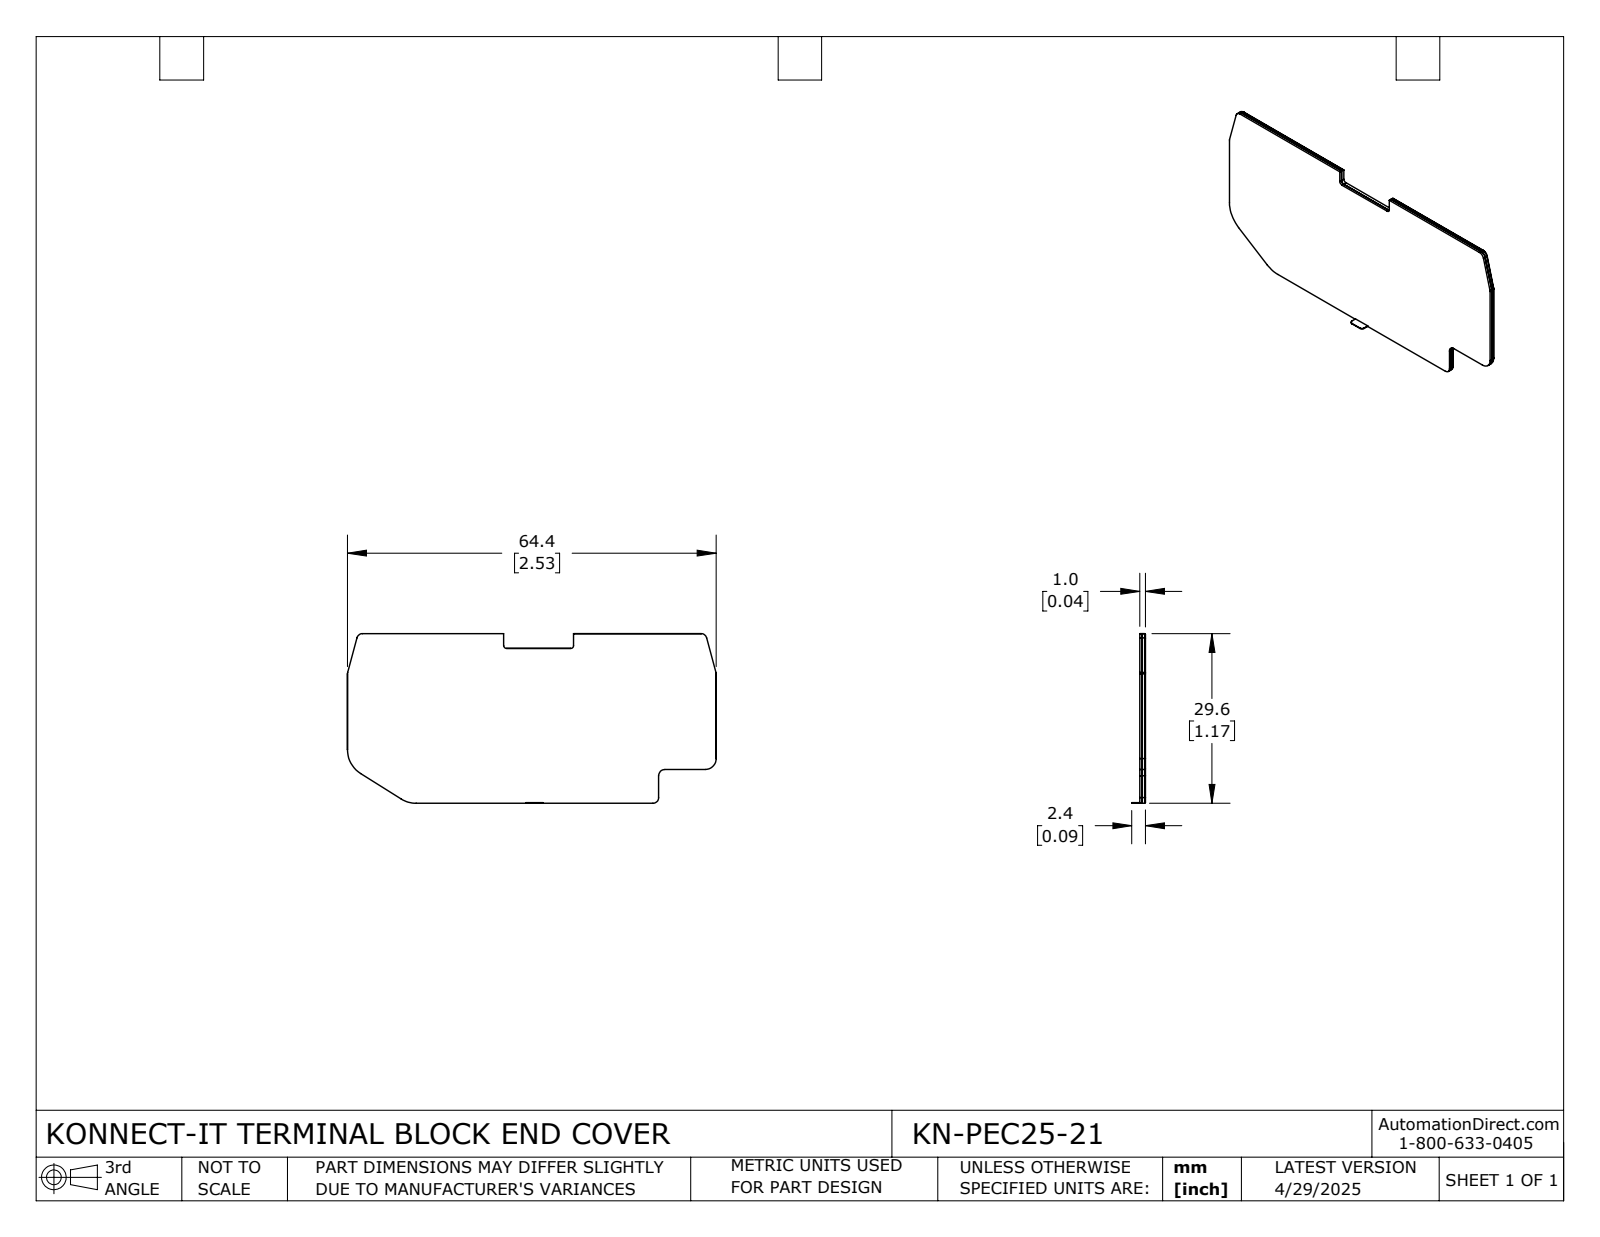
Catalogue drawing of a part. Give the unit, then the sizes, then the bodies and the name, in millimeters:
Units: millimetres
Overall size (bounding box): 64.37 × 29.61 × 2.4
Partial cylindrical surfaces — rounded edges, fillets, slot ends (radius × count): R0.9 ×5, R1 ×5, R0.5 ×4, R4.8 ×2, R4.9 ×2, R1.1 ×1, R1.2 ×1, R1.8 ×1
Main face-to-face distances: 0.42, 1, 0.58, 29.61, 29.51, 0.85, 0.43, 64.37, 27.02, 2.59
Volume: 1 763 mm³ · Surface area: 7 252 mm²
Bodies: 2 solids, 78 faces (45 planar, 33 cylindrical, 0 other)
Part name (STEP PRODUCT): KN-PEC25-21
STEP written by: SolidWorks 2024 (CONFIG_CONTROL_DESIGN)
